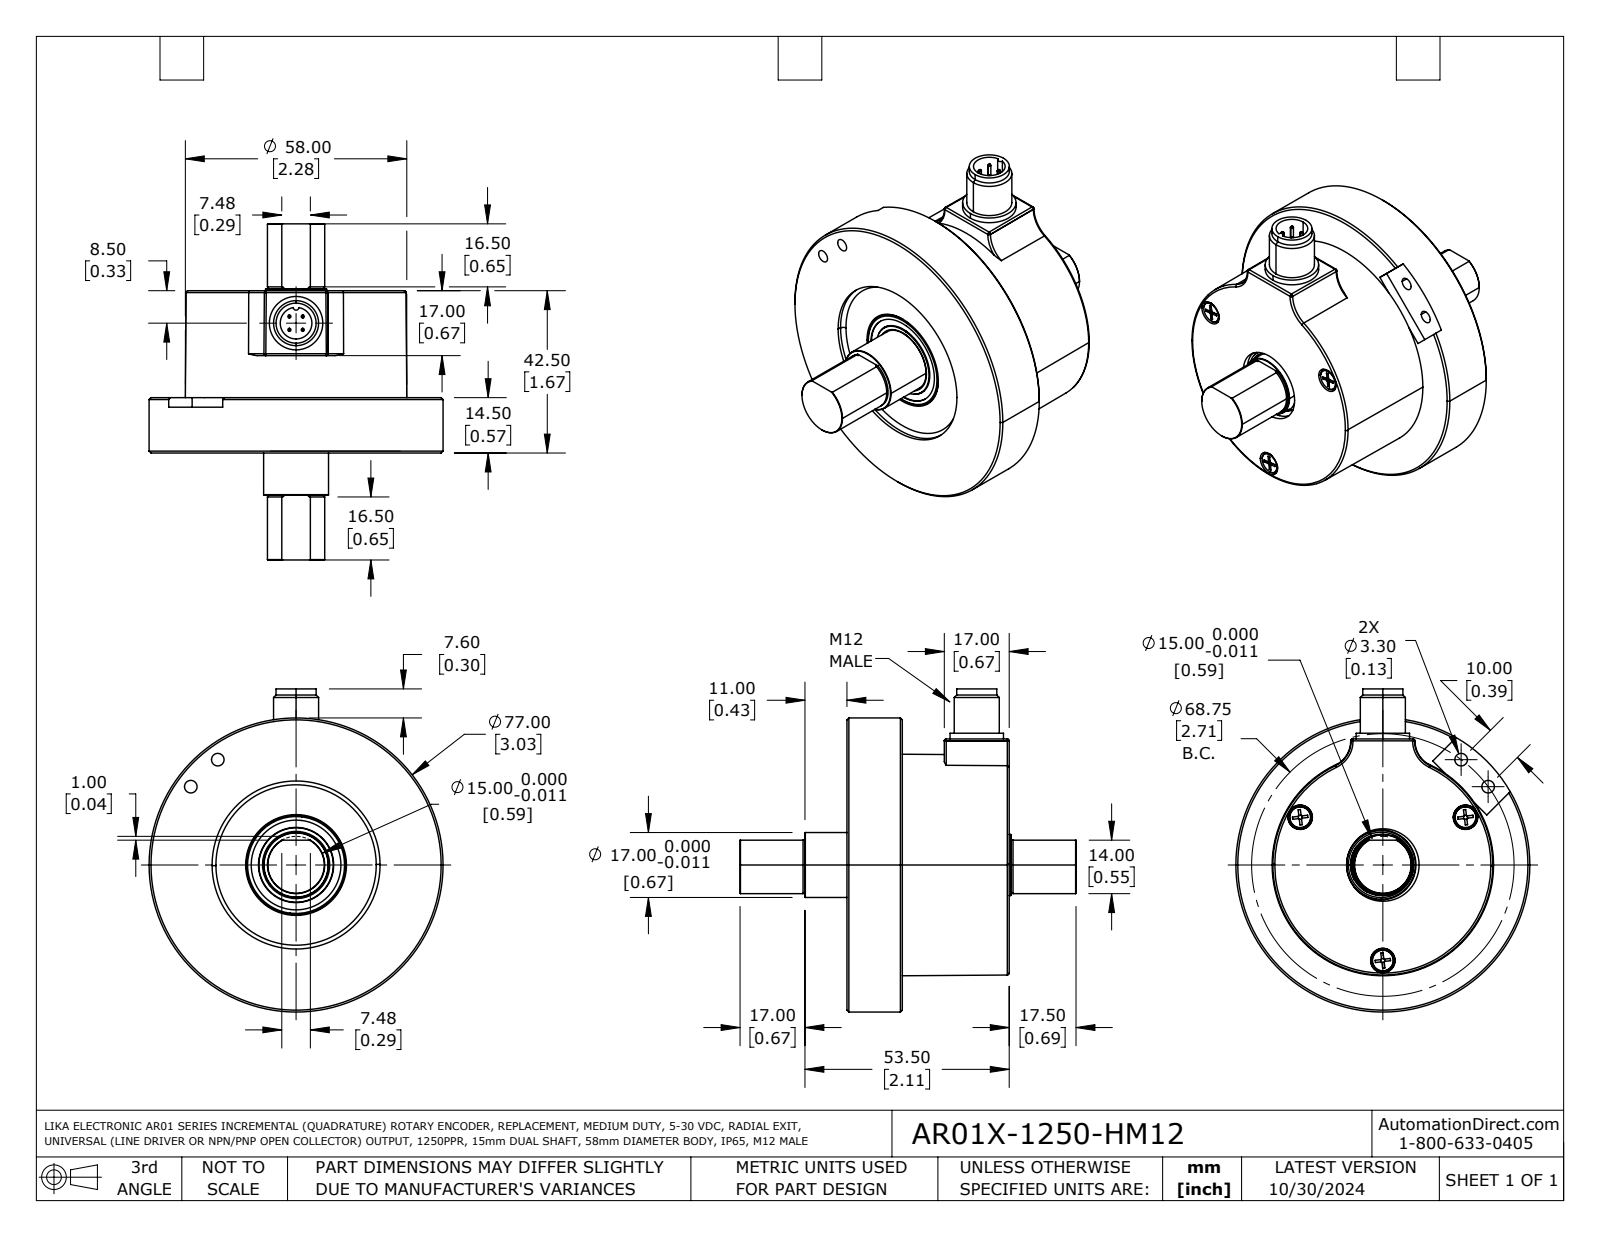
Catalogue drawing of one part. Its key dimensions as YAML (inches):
part_name: "AR01X-1250-HM12"
step_written_by: "SolidWorks 2021 (AUTOMOTIVE_DESIGN)"
units: inches
bodies: {solids: 10, faces: 1346, planar: 838, cylindrical: 204, other: 304}
overall_size: [3.465, 3.331, 3.031]
volume: 5.64
surface_area: 64.82
round_holes:
  - {diameter: 0.098, count: 6}
  - {diameter: 0.13, count: 2}
  - {diameter: 0.315, count: 1}
  - {diameter: 0.327, count: 1}
  - {diameter: 0.394, count: 1}
  - {diameter: 0.413, count: 1}
  - {diameter: 0.748, count: 1}
  - {diameter: 0.776, count: 1}
  - {diameter: 0.917, count: 1}
  - {diameter: 0.925, count: 1}
  - {diameter: 0.927, count: 1}
  - {diameter: 0.945, count: 1}
round_bosses_or_shafts:
  - {diameter: 0.055, count: 4}
  - {diameter: 0.031, count: 4}
  - {diameter: 0.118, count: 3}
  - {diameter: 3.031, count: 1}
  - {diameter: 2.205, count: 1}
  - {diameter: 2.106, count: 1}
  - {diameter: 0.945, count: 1}
  - {diameter: 0.906, count: 1}
partial_cylinders:
  - {radius: 0.007, count: 9}
  - {radius: 0.02, count: 9}
  - {radius: 0.008, count: 3}
  - {radius: 0.03, count: 3}
  - {radius: 0.079, count: 1}
  - {radius: 0.236, count: 1}
face_to_face_distances: [1.673, 1.102, 0.571, 0.118, 0.689, 0.984, 1.043, 0.925, 0.059, 0.614]
hole_center_spacings: [0.984, 1.705, 0.342, 1.353, 0.019, 0.392, 0.394, 0.426]
